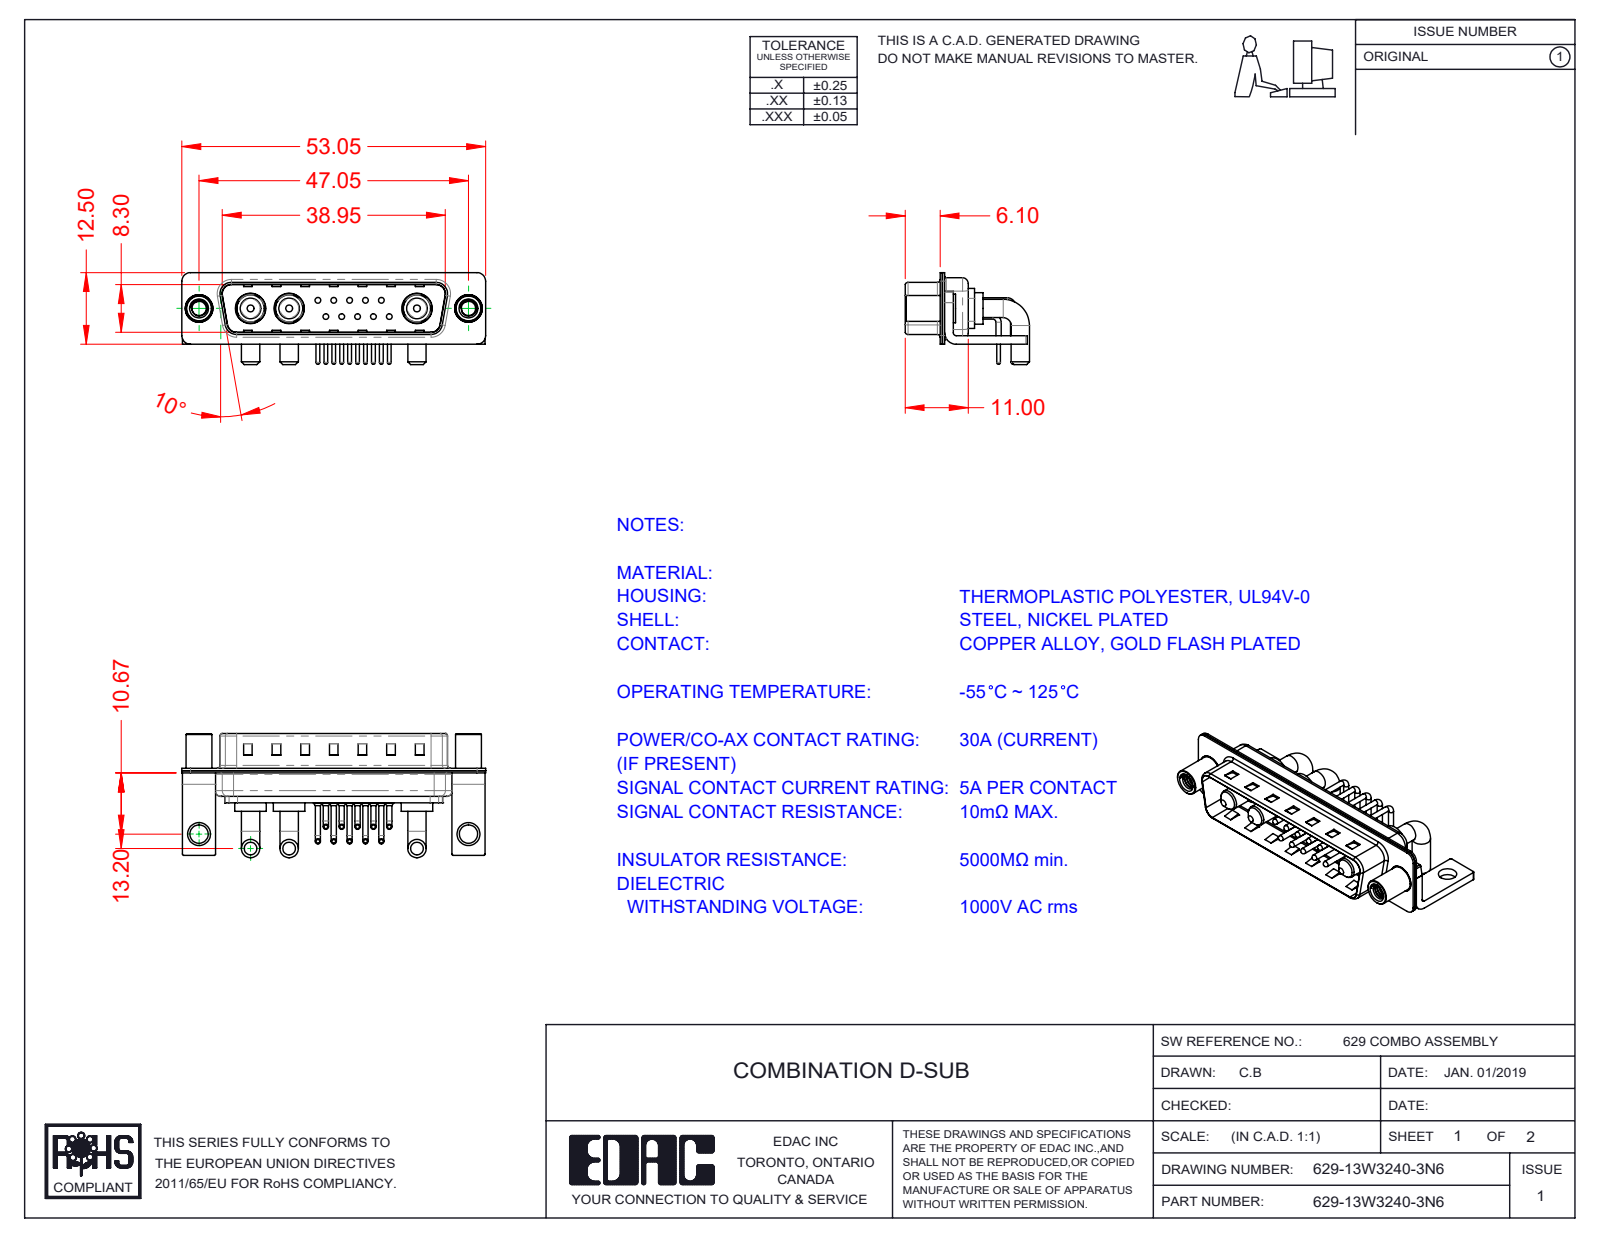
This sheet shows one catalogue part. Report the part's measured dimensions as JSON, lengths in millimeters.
{"part_name": "629Combo Threaded Standoff_D; 629Combo Shell Rear_25 Contacts; Power Pin_30A RA; 629Combo Housing_13W3 (+5 more)", "step_written_by": "SolidWorks 2020 (CONFIG_CONTROL_DESIGN)", "units": "millimeters", "bodies": {"solids": 23, "faces": 1703, "planar": 863, "cylindrical": 632, "other": 208}, "overall_size": [53.05, 21.7, 16.05], "volume_mm3": 3678, "surface_area_mm2": 8351, "round_holes": [[0.75, 10], [1.6, 10], [2, 10], [4.85, 3], [5.3, 3], [2.5, 2], [3.2, 2], [4, 2], [4.8, 2]], "round_bosses_or_shafts": [[0.9, 20], [1.5, 10], [1, 10], [0.65, 10], [3.2, 6], [5.5, 3], [5.2, 3], [4.75, 3]], "partial_cylinders_radius": [[0.25, 16], [1.5, 16], [2, 13], [1.01, 10], [0.5, 9], [1.6, 8], [0.6, 4], [0.65, 4]], "face_to_face_distances": [0.4, 0.8, 9.5, 1.5, 9.1, 8.7, 9.9, 5.2, 0.6, 5.6], "hole_center_spacings": [3.16, 2.77, 5.04, 5.54, 7.49, 5.03, 8.31, 10.11]}
